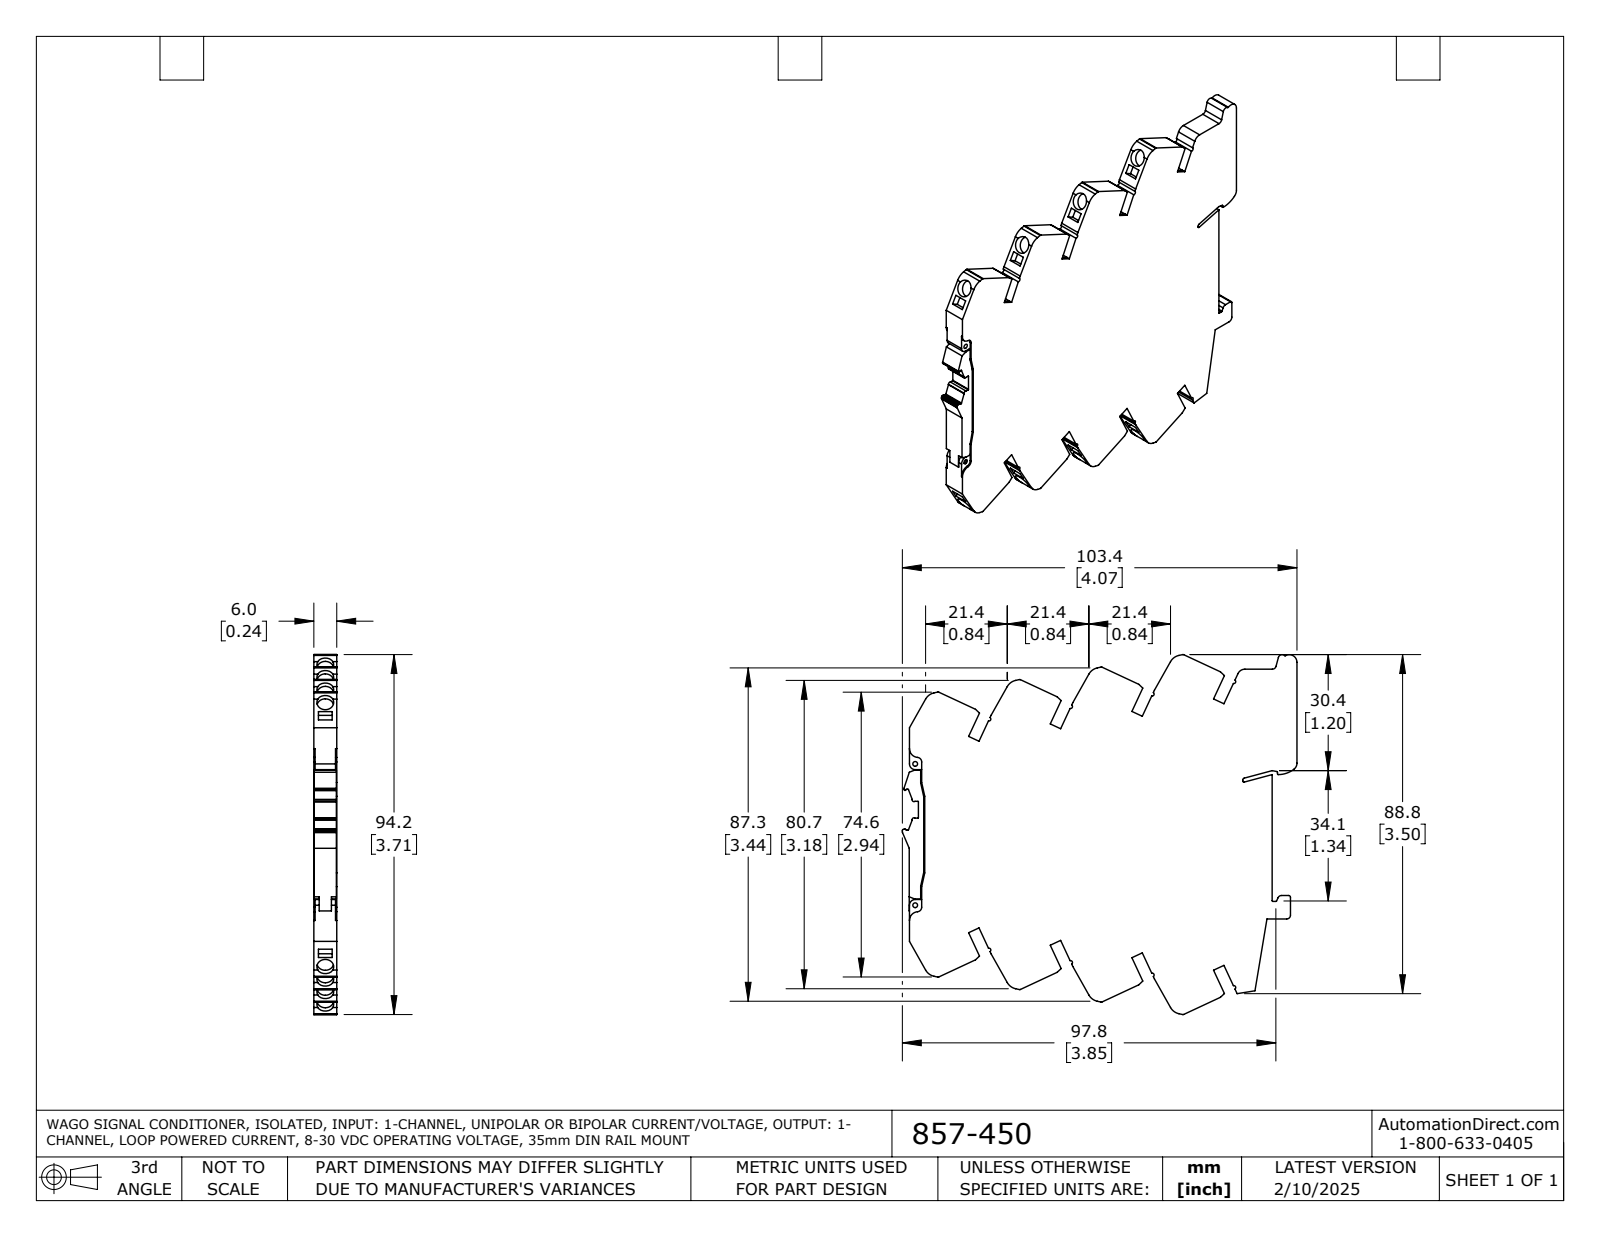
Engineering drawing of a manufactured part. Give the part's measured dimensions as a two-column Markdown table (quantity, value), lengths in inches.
| quantity | value |
| --- | --- |
| part name | 857-450 |
| STEP written by | SolidWorks 2021 (AUTOMOTIVE_DESIGN) |
| units | inches |
| bodies | 1 solid, 317 faces (219 planar, 98 cylindrical, 0 other) |
| overall size | 4.069 × 3.711 × 0.236 |
| volume | 2.681 in³ |
| surface area | 29.86 in² |
| round holes (diameter × count) | 0.173 × 8, 0.049 × 2 |
| partial cylindrical surfaces (radius × count) | 0.02 × 12, 0.008 × 11, 0.016 × 8, 0.132 × 8, 0.039 × 4, 0.012 × 3, 0.079 × 3, 0.018 × 2 |
| main face-to-face distances | 0.236, 0.708, 0.67, 0.473, 0.232, 0.472, 0.118, 0.945, 1.417, 0.256 |
| hole center spacings | 0.526, 0.525, 1.051, 1.051, 1.052, 1.457, 1.576, 1.577 |
